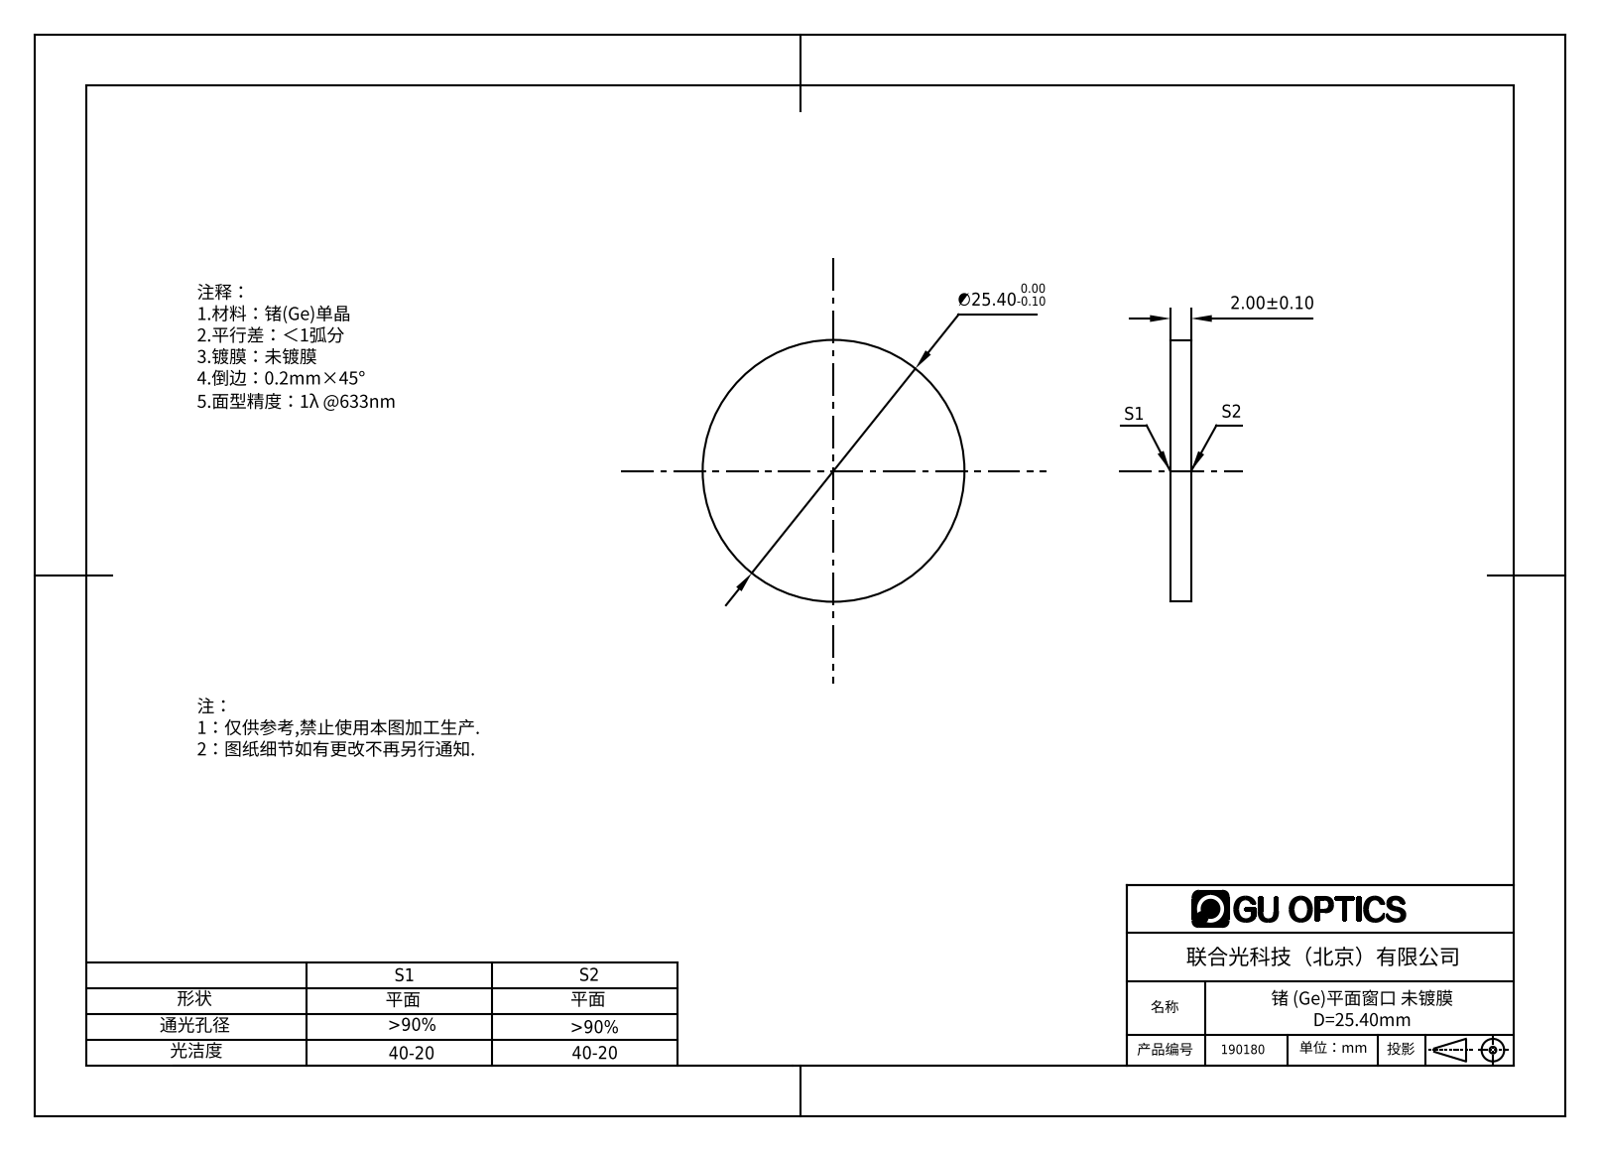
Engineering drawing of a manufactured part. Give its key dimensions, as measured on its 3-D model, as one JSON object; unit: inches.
{"part_name": "190166", "step_written_by": "SolidWorks 2016 (AUTOMOTIVE_DESIGN)", "units": "inches", "bodies": {"solids": 1, "faces": 4, "planar": 2, "cylindrical": 2, "other": 0}, "overall_size": [1, 1, 0.079], "volume_in3": 0.062, "surface_area_in2": 1.818, "round_bosses_or_shafts": [[1, 1]], "face_to_face_distances": [0.079]}
